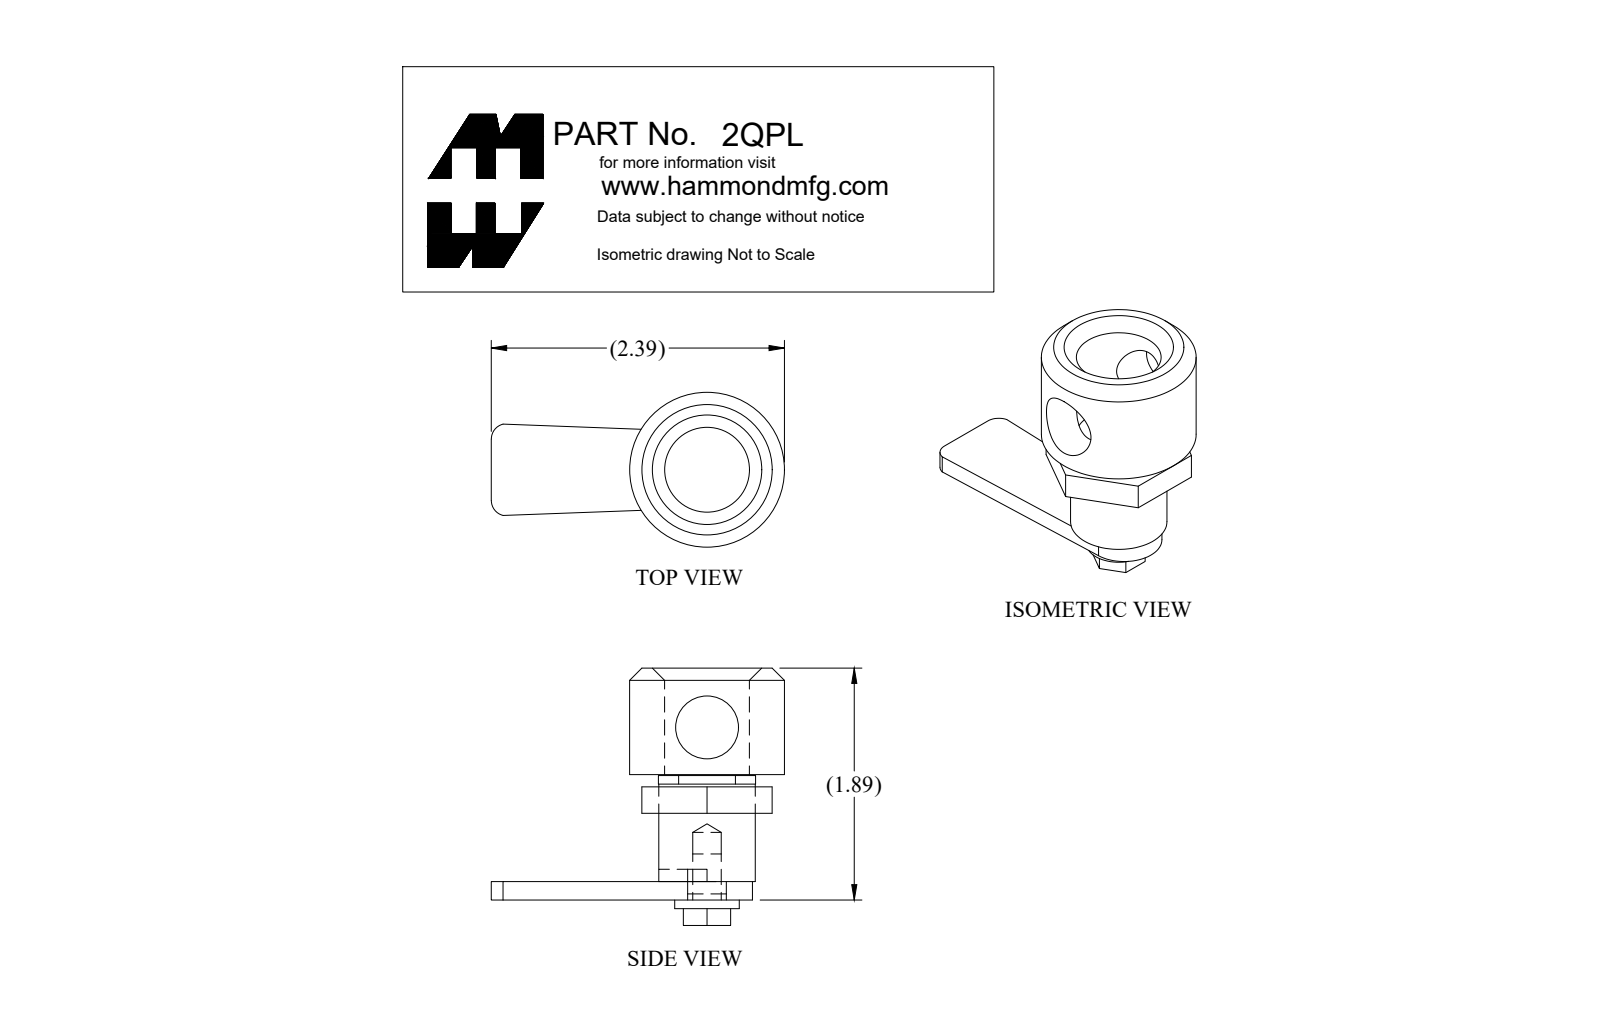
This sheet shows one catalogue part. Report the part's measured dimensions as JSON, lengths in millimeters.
{"part_name": "2QPL", "step_written_by": "SolidWorks 2018 (AUTOMOTIVE_DESIGN)", "units": "millimeters", "bodies": {"solids": 5, "faces": 63, "planar": 48, "cylindrical": 12, "other": 3}, "overall_size": [60.6, 53.2, 32], "volume_mm3": 22140, "surface_area_mm2": 11280, "round_holes": [[5.9, 1], [13, 1], [17.5, 1], [19.9, 1]], "round_bosses_or_shafts": [[32, 1], [13.3, 1]], "partial_cylinders_radius": [[3.2, 2], [7.8, 1]], "face_to_face_distances": [3.8, 22.1, 25.9, 25.7, 8, 2.5, 19.6, 21.9, 23.4, 2.3]}
